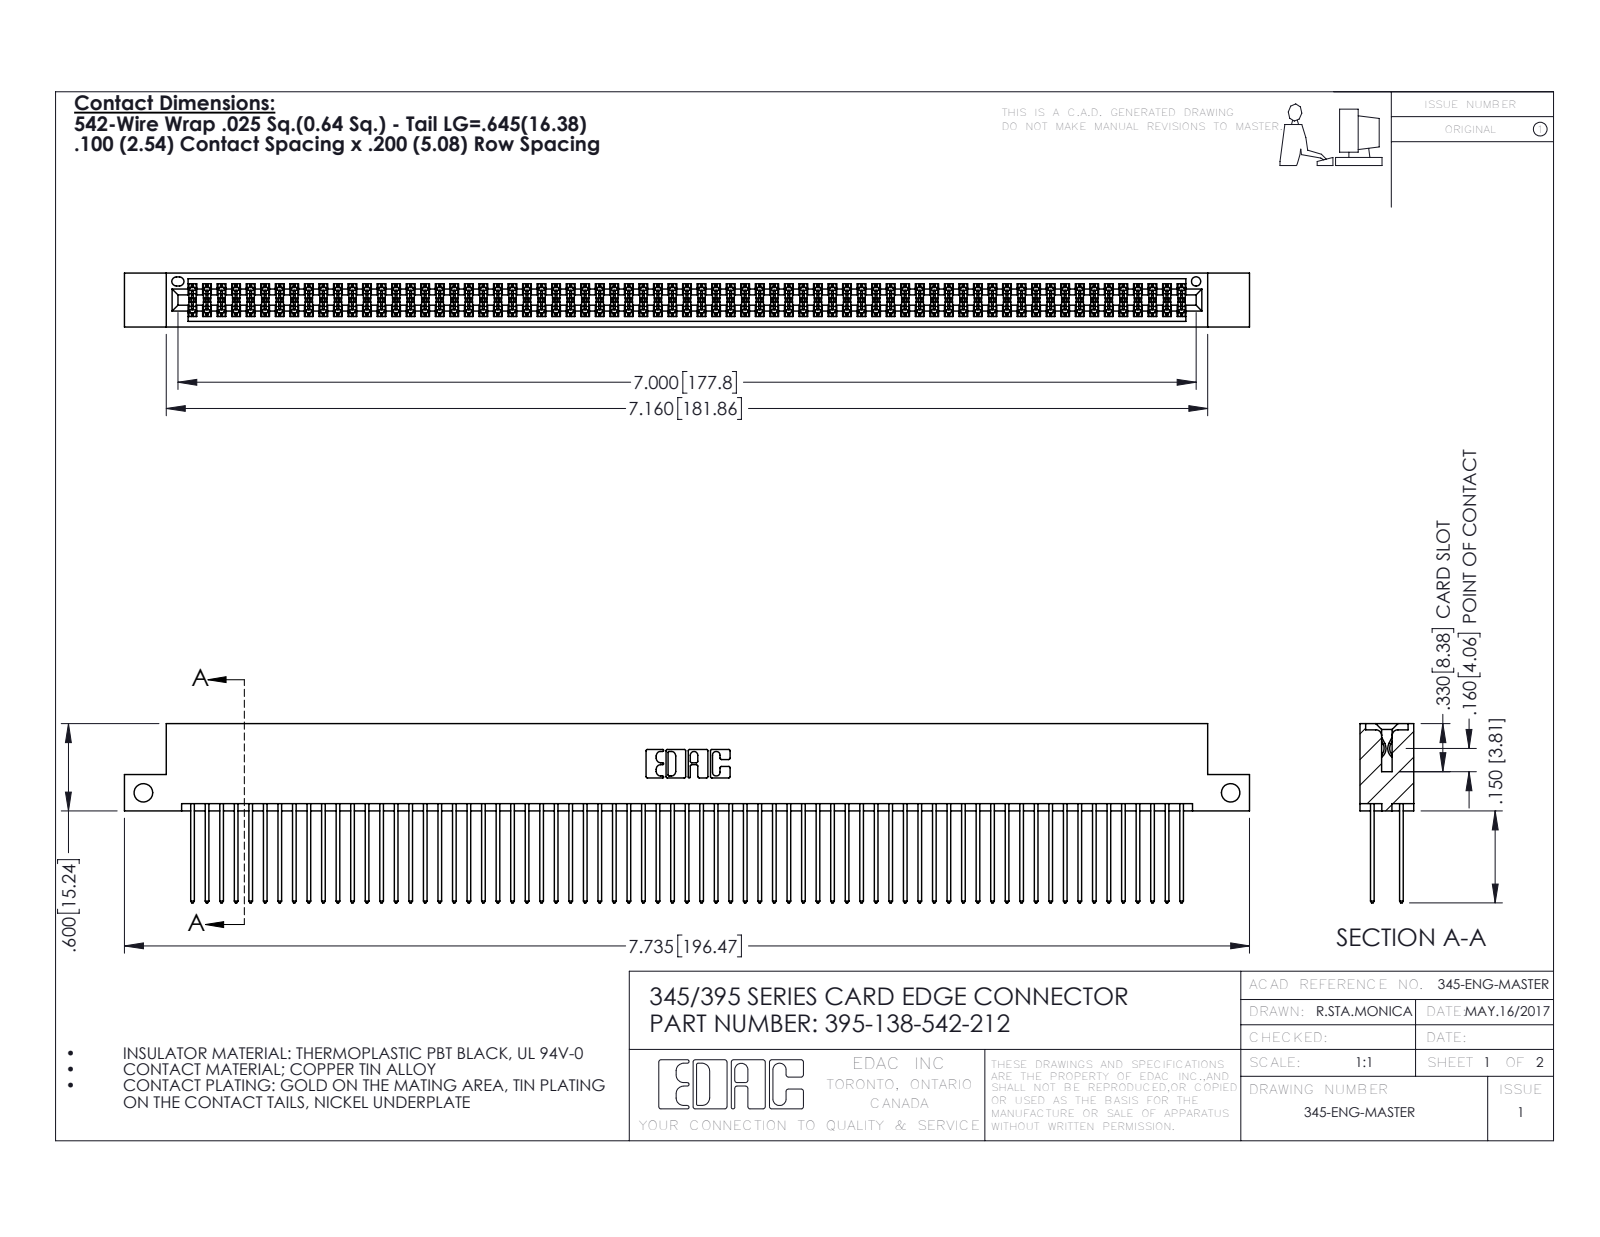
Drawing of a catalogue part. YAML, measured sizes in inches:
part_name: "345 Part_Flush Mounting Lugs - Side Mount; 395-138-542-212; 345-292-001_345-293-142"
step_written_by: "SolidWorks 2016 (CONFIG_CONTROL_DESIGN)"
units: inches
bodies: {solids: 139, faces: 7026, planar: 4634, cylindrical: 2392, other: 0}
overall_size: [7.735, 1.232, 0.37]
volume: 1.214
surface_area: 50.84
round_holes:
  - {diameter: 0.128, count: 2}
  - {diameter: 0.064, count: 1}
partial_cylinders:
  - {radius: 0.006, count: 207}
  - {radius: 0.01, count: 138}
  - {radius: 0.01, count: 22}
  - {radius: 0.007, count: 6}
  - {radius: 0.031, count: 6}
  - {radius: 0.026, count: 3}
  - {radius: 0.014, count: 2}
  - {radius: 0.019, count: 2}
face_to_face_distances: [0.298, 0.072, 0.2, 0.098, 0.272, 0.025, 0.225, 0.37, 0.175, 0.149]
hole_center_spacings: [7.475]
